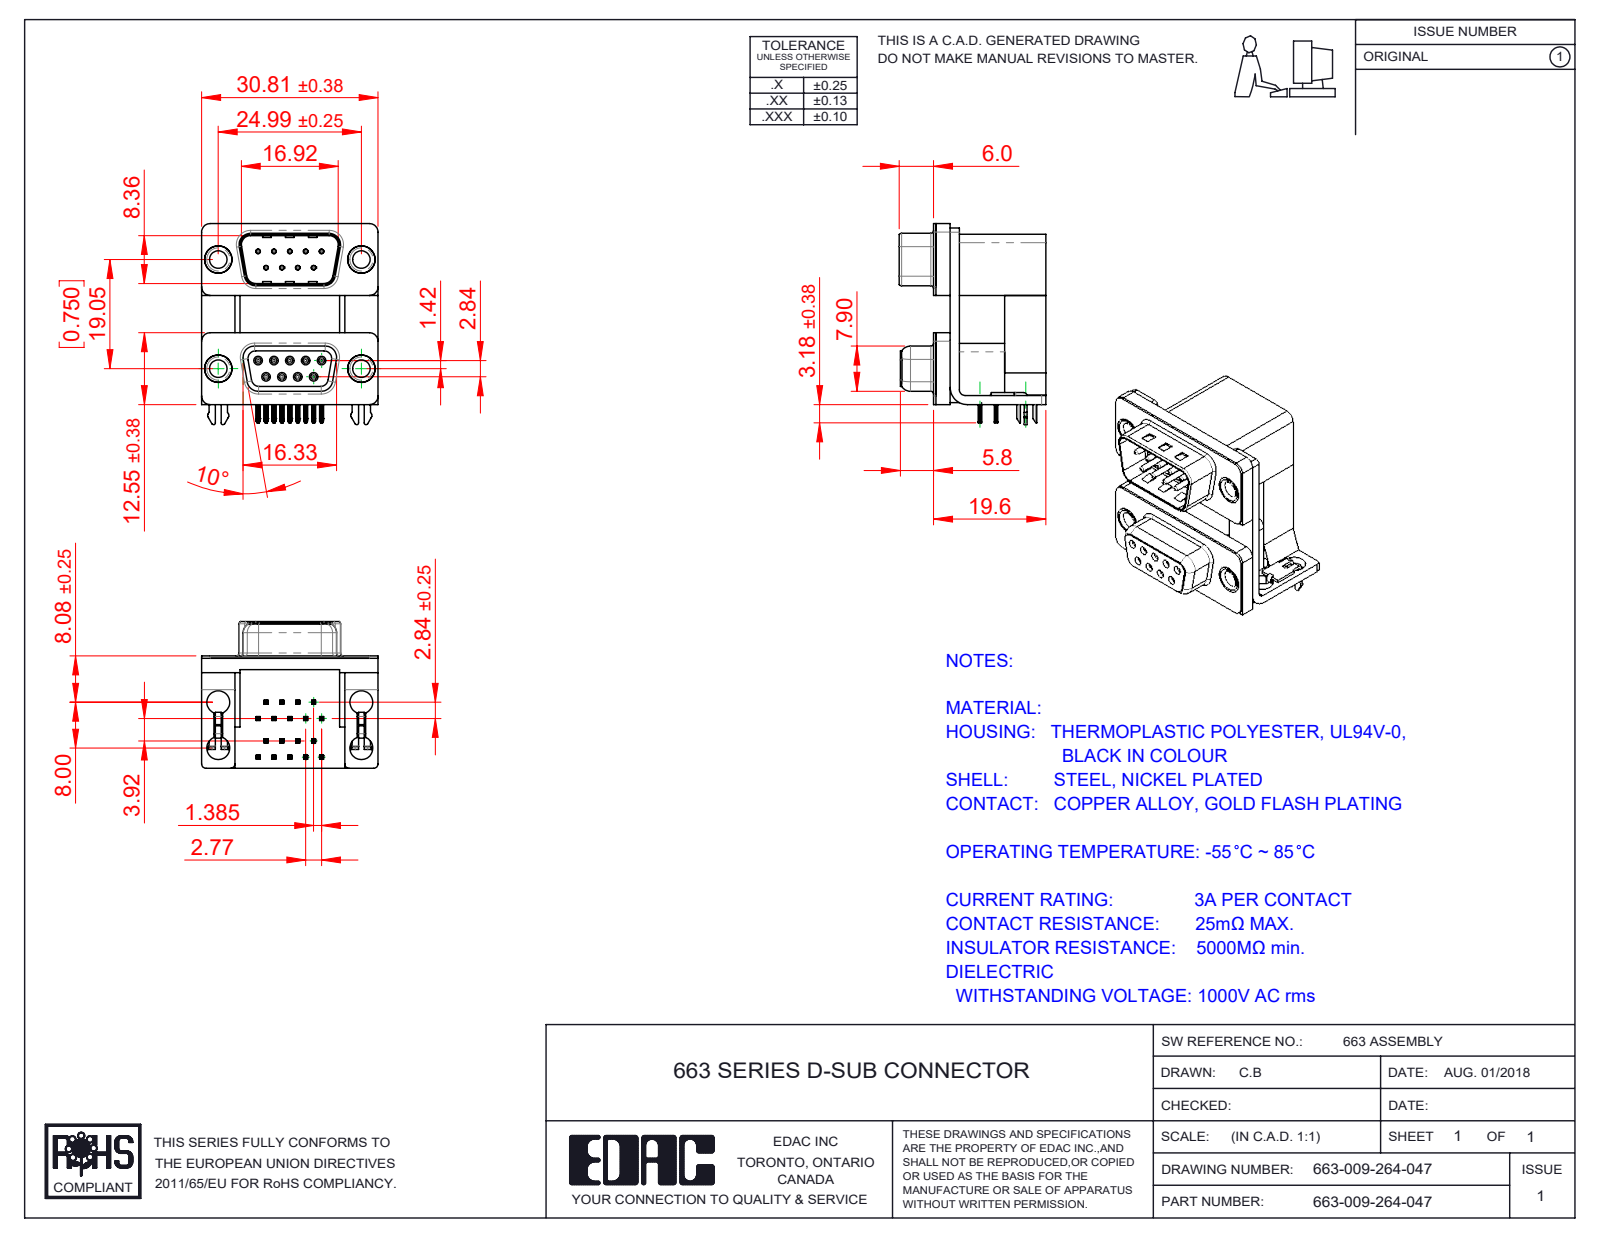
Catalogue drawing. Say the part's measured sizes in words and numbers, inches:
The part is named "663-009-264-047; 663 Housing Spacer_09 Contacts M; 663 Mounting Bracket_2ProngM; 663 Housing Lower_09 Contacts (+8 more)". Its 3-D file was written by "SolidWorks 2020 (CONFIG_CONTROL_DESIGN)". It is 31 solids with 2553 faces: 1341 planar, 689 cylindrical and 523 other. Overall it measures 1.382 by 1.213 by 1.008 inches. Its volume is 0.658 cubic inches and its surface area 19.53 square inches. Round holes: 18 of diameter 0.031, 9 of diameter 0.014, 9 of diameter 0.035, 8 of diameter 0.157, 4 of diameter 0.12, 4 of diameter 0.138, 4 of diameter 0.189, 4 of diameter 0.197. Round bosses or shafts: 9 of diameter 0.047, 9 of diameter 0.03, 4 of diameter 0.193, 4 of diameter 0.187, 4 of diameter 0.152. Partial cylindrical surfaces (rounded edges, fillets, slot ends): 73 of radius 0.004, 42 of radius 0.01, 36 of radius 0.006, 18 of radius 0.005, 18 of radius 0.014, 16 of radius 0.02, 15 of radius 0.059, 10 of radius 0.03. The main face-to-face distances are 0.016, 0.098, 0.657, 0.756, 0.283, 0.374, 0.472, 0.063, 0.772, 0.488. The hole center spacings are 0.124, 0.109, 0.758, 0.75, 0.218, 0.781, 0.641, 0.863.
